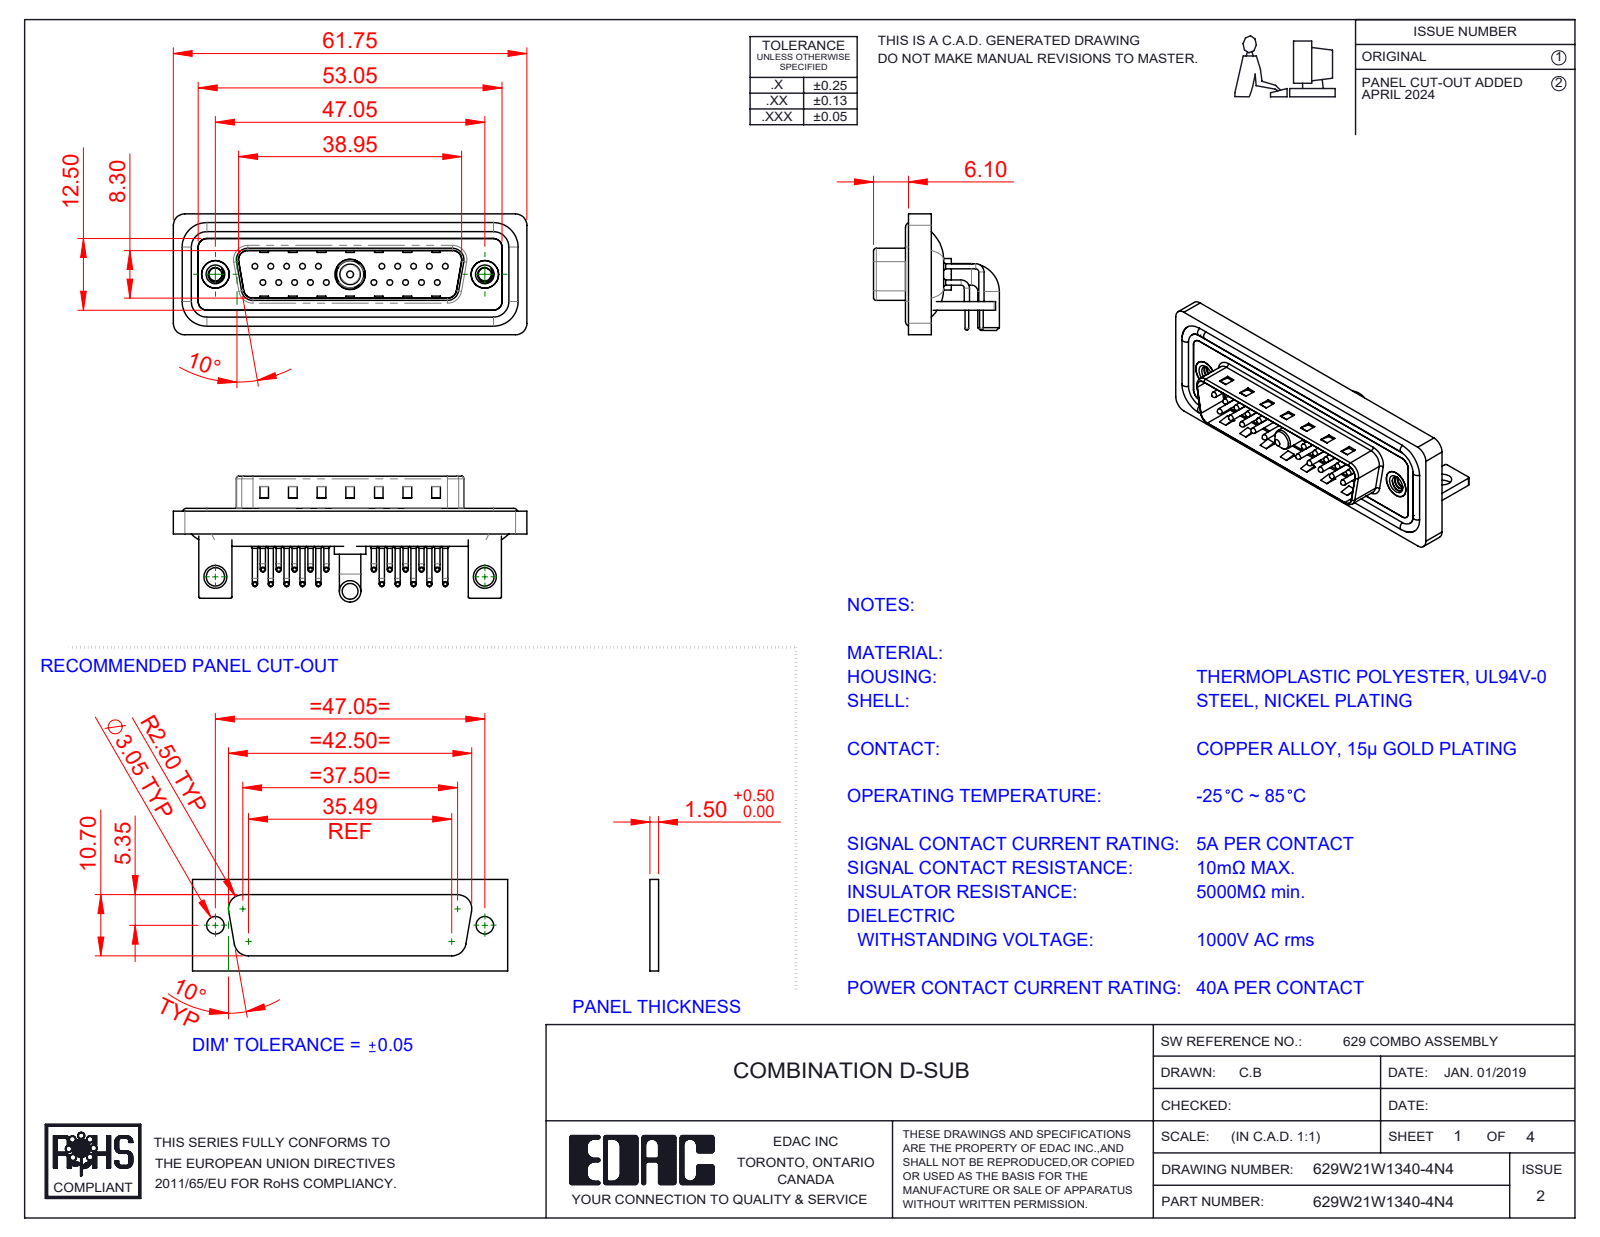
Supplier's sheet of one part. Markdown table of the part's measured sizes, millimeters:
| quantity | value |
| --- | --- |
| part name | 629W21W1340-4N4; 629Combo Threaded Rivet_3; 629Combo Contact Row 1; 629Combo Shell Rear_25 Contacts (+6 more) |
| STEP written by | SolidWorks 2023 (CONFIG_CONTROL_DESIGN) |
| units | millimeters |
| bodies | 31 solids, 2766 faces (1519 planar, 947 cylindrical, 300 other) |
| overall size | 61.75 × 21.98 × 21.1 |
| volume | 7 768 mm³ |
| surface area | 13 352 mm² |
| round holes (diameter × count) | 0.75 × 20, 1.6 × 20, 2 × 20, 2.26 × 2, 3.2 × 2, 4 × 2, 4.8 × 2, 5 × 2, 4.85 × 1, 5.3 × 1 |
| round bosses / shafts (diameter × count) | 0.9 × 40, 1.5 × 20, 1 × 20, 0.65 × 20, 1.6 × 4, 4.9 × 2, 3.75 × 2, 5.5 × 1 |
| partial cylindrical surfaces (radius × count) | 1.01 × 20, 2 × 19, 1.5 × 18, 0.25 × 16, 0.5 × 9, 1.6 × 8, 0.6 × 4, 0.65 × 4 |
| main face-to-face distances | 0.4, 0.8, 2.1, 2.9, 1.5, 1.1, 4.1, 1.6, 4.5, 3.7 |
| hole center spacings | 3.16, 2.77, 5.54, 8.31, 5.04, 19.39, 20.97, 22.16 |
